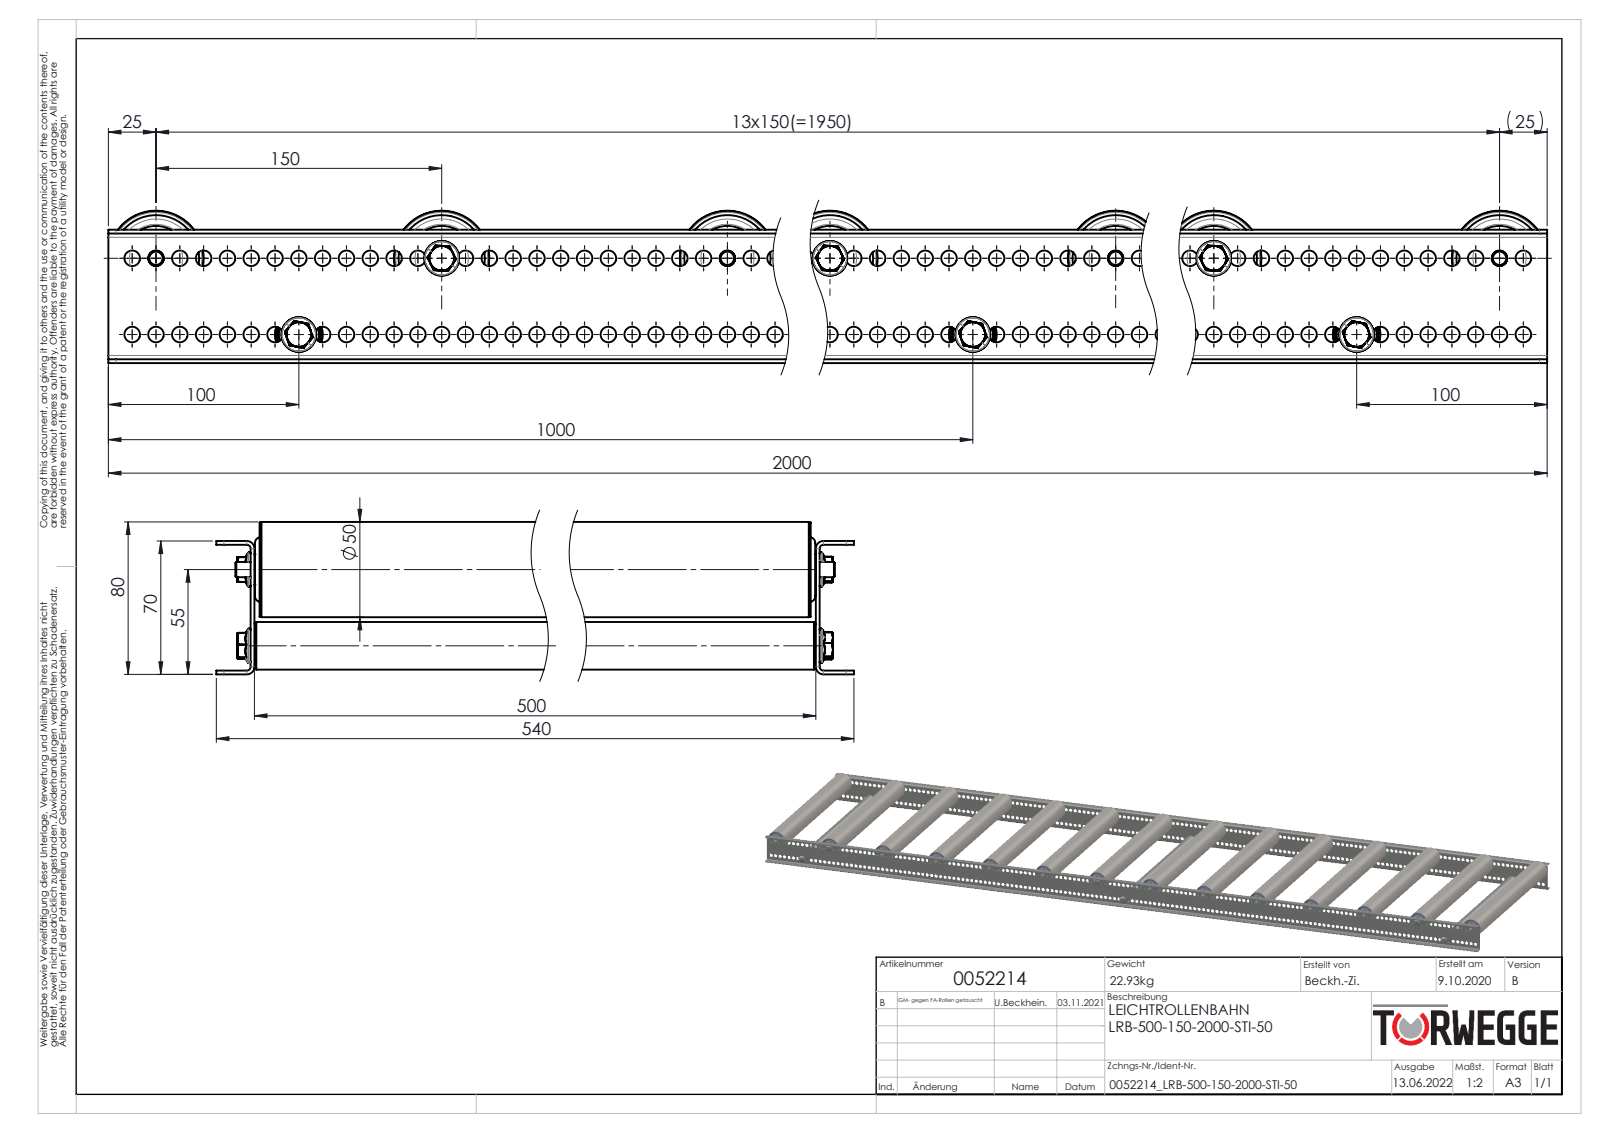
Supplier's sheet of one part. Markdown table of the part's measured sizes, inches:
| quantity | value |
| --- | --- |
| part name | Sicherungsring_DIN471_8x0.8_Circlip DIN 471 - 8 x 0.8; Profil_LRB-20x70x20x2_KFG_S100202_U-PROFIL-20-70-20-2-LRB-L=2000; TRG-50x1,5-STI-A8-FA_KFG_0054466_TRG-50x1,5-STI-A8-FA-EL=500; 0052214 (+8 more) |
| STEP written by | SolidWorks 2020 (AUTOMOTIVE_DESIGN) |
| units | inches |
| bodies | 350 solids, 6934 faces (1320 planar, 2752 cylindrical, 2862 other) |
| overall size | 78.74 × 21.26 × 3.15 |
| volume | 201.8 in³ |
| surface area | 5 836 in² |
| round holes (diameter × count) | 0.323 × 318, 0.673 × 14, 0.728 × 14, 1.091 × 14, 1.783 × 14, 1.85 × 14, 0.299 × 11, 0.268 × 6, 0.472 × 3, 0.48 × 3, 0.756 × 3, 0.827 × 3 |
| round bosses / shafts (diameter × count) | 0.315 × 17, 1.969 × 14, 1.949 × 14, 1.862 × 14, 1.169 × 14, 1.079 × 14, 1.075 × 14, 0.63 × 14 |
| partial cylindrical surfaces (radius × count) | 0.024 × 22, 0.03 × 22, 0.096 × 22, 0.098 × 12, 0.192 × 11, 0.276 × 11, 0.157 × 8, 0.079 × 4 |
| main face-to-face distances | 0.079, 19.764, 2.677, 19.685, 19.843, 2.756, 2.598, 0.709, 0.787, 20.472 |
| hole center spacings | 0.492, 0.984, 1.476, 1.969, 2.461, 2.953, 3.445, 3.937 |
